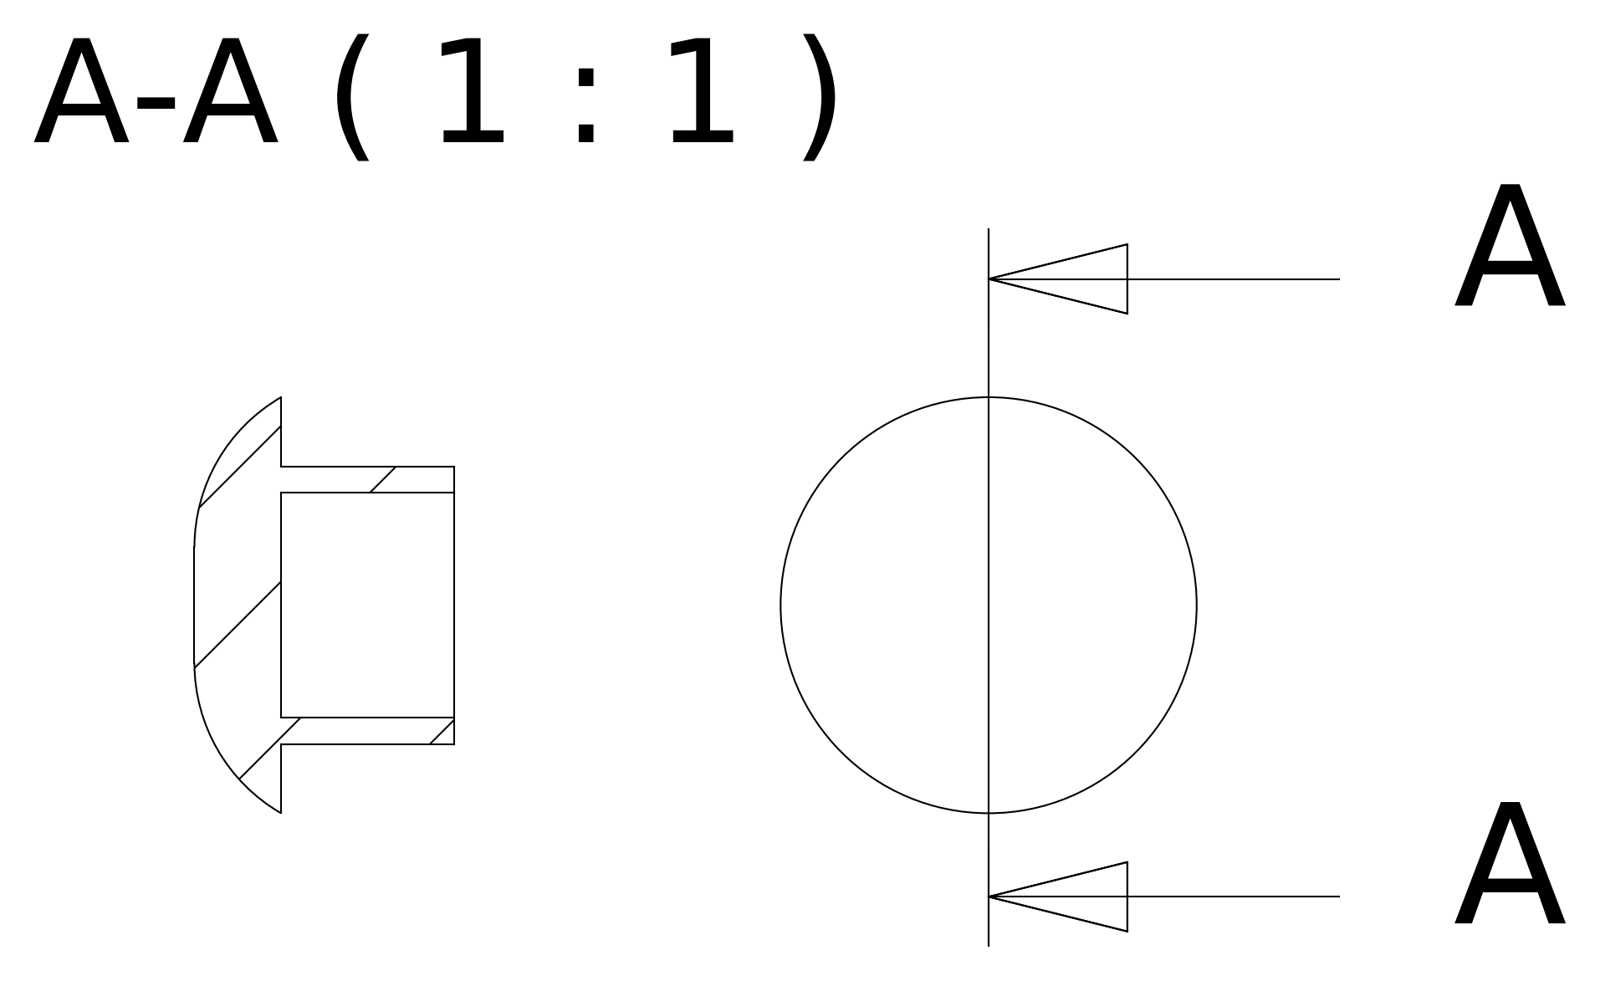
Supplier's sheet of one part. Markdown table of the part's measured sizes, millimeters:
| quantity | value |
| --- | --- |
| part name | 440000010079 |
| STEP written by | Autodesk Inventor 2016 (AUTOMOTIVE_DESIGN) |
| units | millimeters |
| bodies | 1 solid, 7 faces (4 planar, 2 cylindrical, 1 other) |
| overall size | 12 × 12 × 7.5 |
| volume | 270 mm³ |
| surface area | 483 mm² |
| round holes (diameter × count) | 6.5 × 1 |
| round bosses / shafts (diameter × count) | 8 × 1 |
| main face-to-face distances | 5, 7.5, 2.5 |
